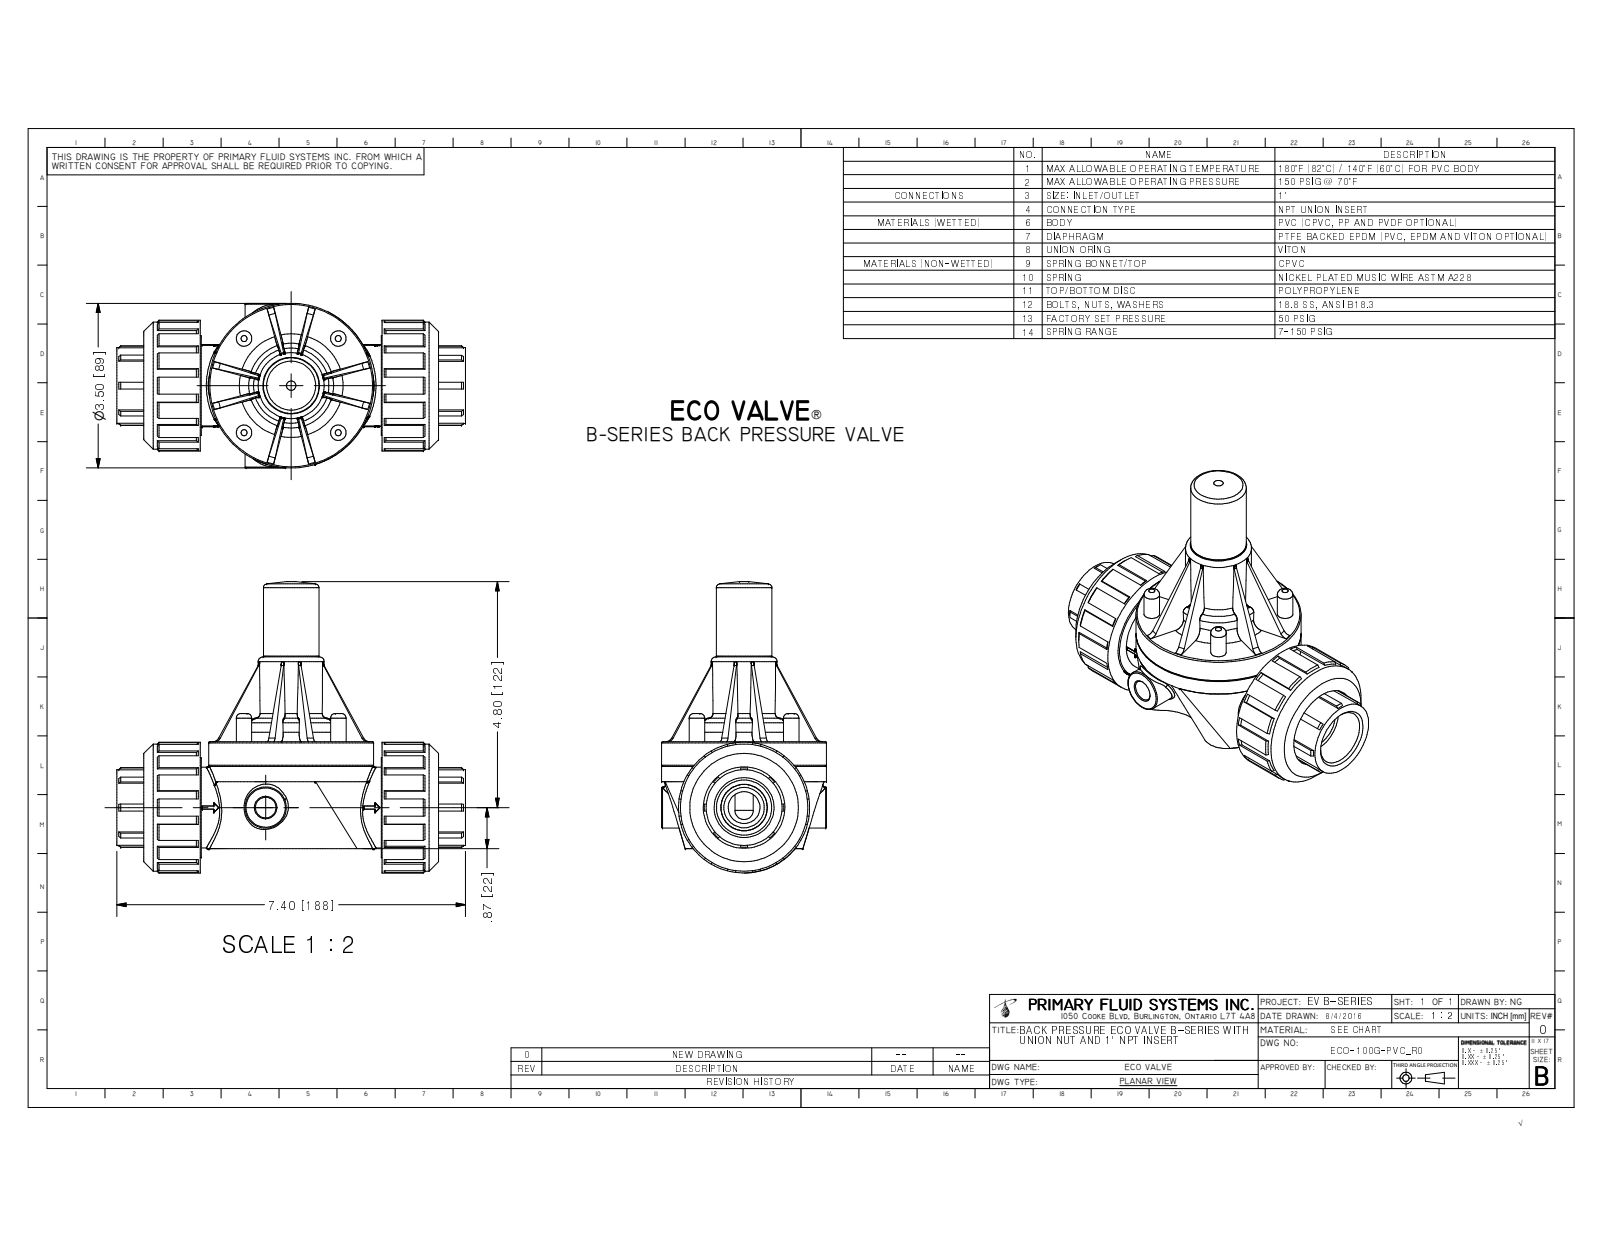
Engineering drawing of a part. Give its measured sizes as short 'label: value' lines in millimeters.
name: ECO-100G-PVC_R0
written by: Autodesk Inventor 2009 (AUTOMOTIVE_DESIGN)
unit: mm
bodies: 1 solid, 548 faces (243 planar, 112 cylindrical, 193 other)
size: 187.9 × 157.3 × 88.9
volume: 664 200 mm³; area: 97 100 mm²
holes: 4× ⌀5.8, 4× ⌀6.5, 4× ⌀10.2, 1× ⌀6.5, 1× ⌀11.1, 1× ⌀29.7, 1× ⌀43.9
bosses: 4× ⌀8.4, 3× ⌀6.5, 1× ⌀88.9, 1× ⌀70.6, 1× ⌀68.6, 1× ⌀53.8, 1× ⌀45.7, 1× ⌀43.6
rounds: 8× R2.5, 8× R3.8, 4× R1.3, 3× R3.3, 1× R10.6, 1× R13.1, 1× R17, 1× R21.5
face distances: 57.8, 98.1, 30.9, 127.9, 27.4, 125.5, 30.4, 128.4, 158.8, 128.4
hole spacings: 50.8, 71.8, 50.8, 50.8, 71.8, 71.9
